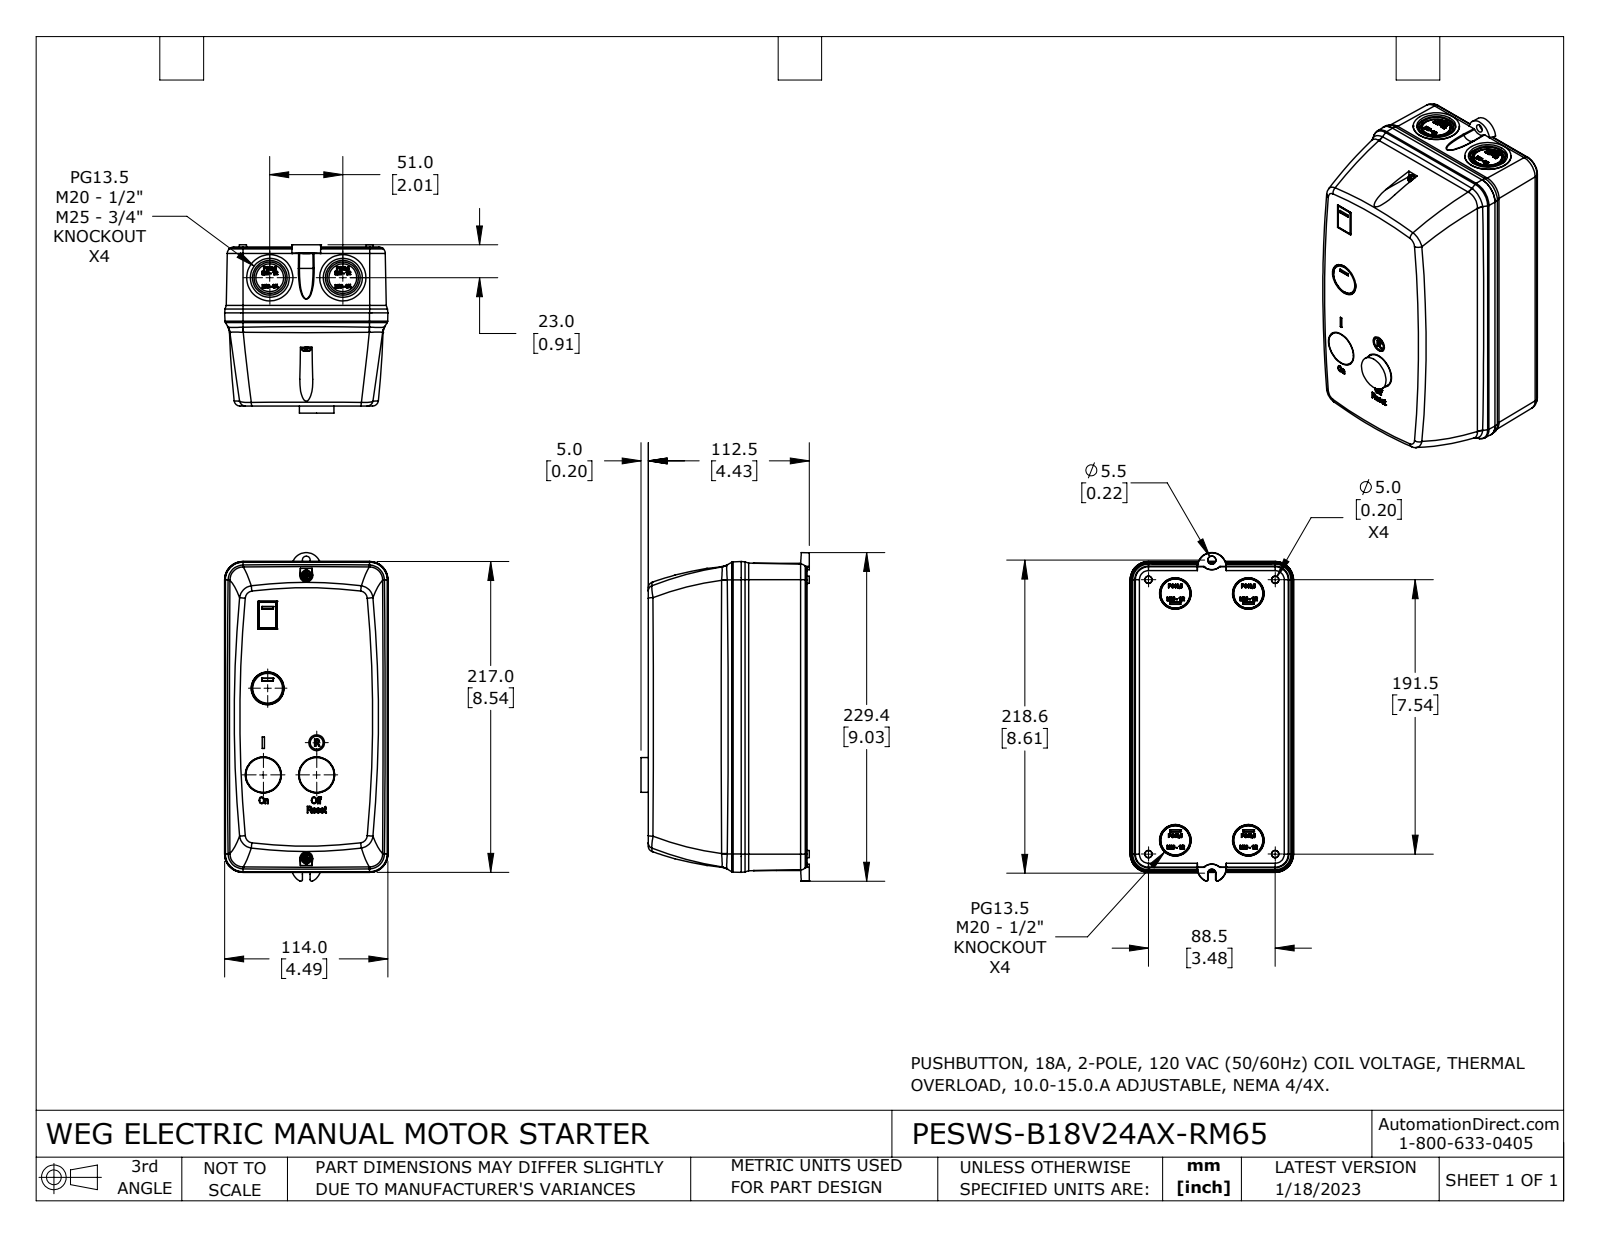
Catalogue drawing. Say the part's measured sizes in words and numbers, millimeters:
The part is named "PESWS-B18V24AX-RM65". Its 3-D file was written by "SolidWorks 2021 (CONFIG_CONTROL_DESIGN)". It is 6 solids with 2195 faces: 1110 planar, 92 cylindrical and 993 other. Overall it measures 229.44 by 117.5 by 114.01 millimeters. Its volume is 2 457 000 cubic millimeters and its surface area 166 196 square millimeters. Round holes: 2 of diameter 4.4, 2 of diameter 21.91, 2 of diameter 27.24, 1 of diameter 5.5, 1 of diameter 11. Round bosses or shafts: 2 of diameter 32.26, 2 of diameter 24.25, 2 of diameter 24.2, 2 of diameter 19.37, 2 of diameter 7, 2 of diameter 3, 1 of diameter 9. Partial cylindrical surfaces (rounded edges, fillets, slot ends): 4 of radius 2, 4 of radius 4.61, 4 of radius 9.54, 2 of radius 6.54, 2 of radius 7.54, 1 of radius 2.08, 1 of radius 2.17, 1 of radius 2.75. The main face-to-face distances are 46, 65, 111, 0.5, 110.5, 45.5, 110, 1, 109.5, 64. The hole center spacings are 10.5, 51, 81.32, 117.22, 127.71, 198, 208.5.
